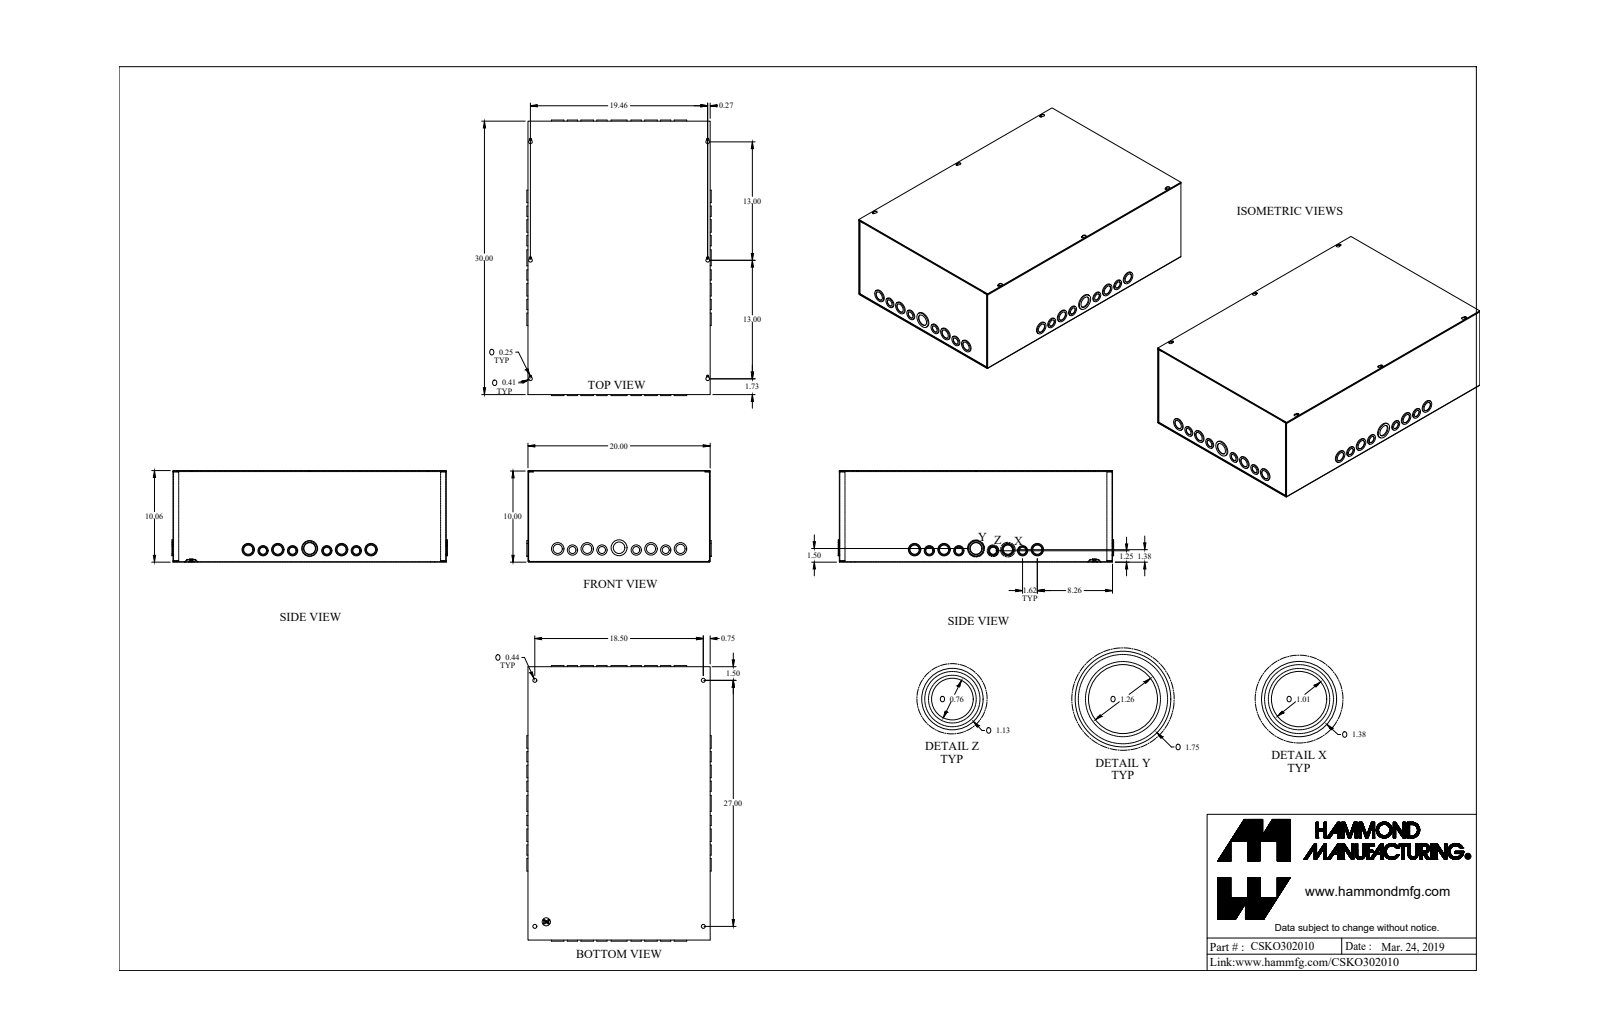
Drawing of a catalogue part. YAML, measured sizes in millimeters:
part_name: "CSKO302010_Default"
step_written_by: "SolidWorks 2019 (CONFIG_CONTROL_DESIGN)"
units: millimeters
bodies: {solids: 4, faces: 653, planar: 273, cylindrical: 372, other: 8}
overall_size: [767.9, 513.9, 255.4]
volume: 2143000
surface_area: 2975000
round_holes:
  - {diameter: 25.7, count: 16}
  - {diameter: 32, count: 10}
  - {diameter: 19.3, count: 8}
  - {diameter: 4.3, count: 7}
  - {diameter: 11.1, count: 4}
  - {diameter: 41.6, count: 2}
  - {diameter: 12.7, count: 1}
round_bosses_or_shafts:
  - {diameter: 28.6, count: 14}
  - {diameter: 34.9, count: 9}
  - {diameter: 22.2, count: 8}
  - {diameter: 22.2, count: 6}
  - {diameter: 28.6, count: 4}
  - {diameter: 44.5, count: 2}
  - {diameter: 34.9, count: 1}
  - {diameter: 12.5, count: 1}
partial_cylinders:
  - {radius: 0.7, count: 12}
  - {radius: 2.2, count: 12}
  - {radius: 1.4, count: 8}
  - {radius: 3.2, count: 6}
  - {radius: 5.2, count: 6}
face_to_face_distances: [1.4, 254, 252.6, 255.4, 506.6, 760.6, 508, 505.1, 762, 759.1]
hole_center_spacings: [41.3, 82.3, 219, 177.8, 260.1, 17.6, 48.2, 89]
